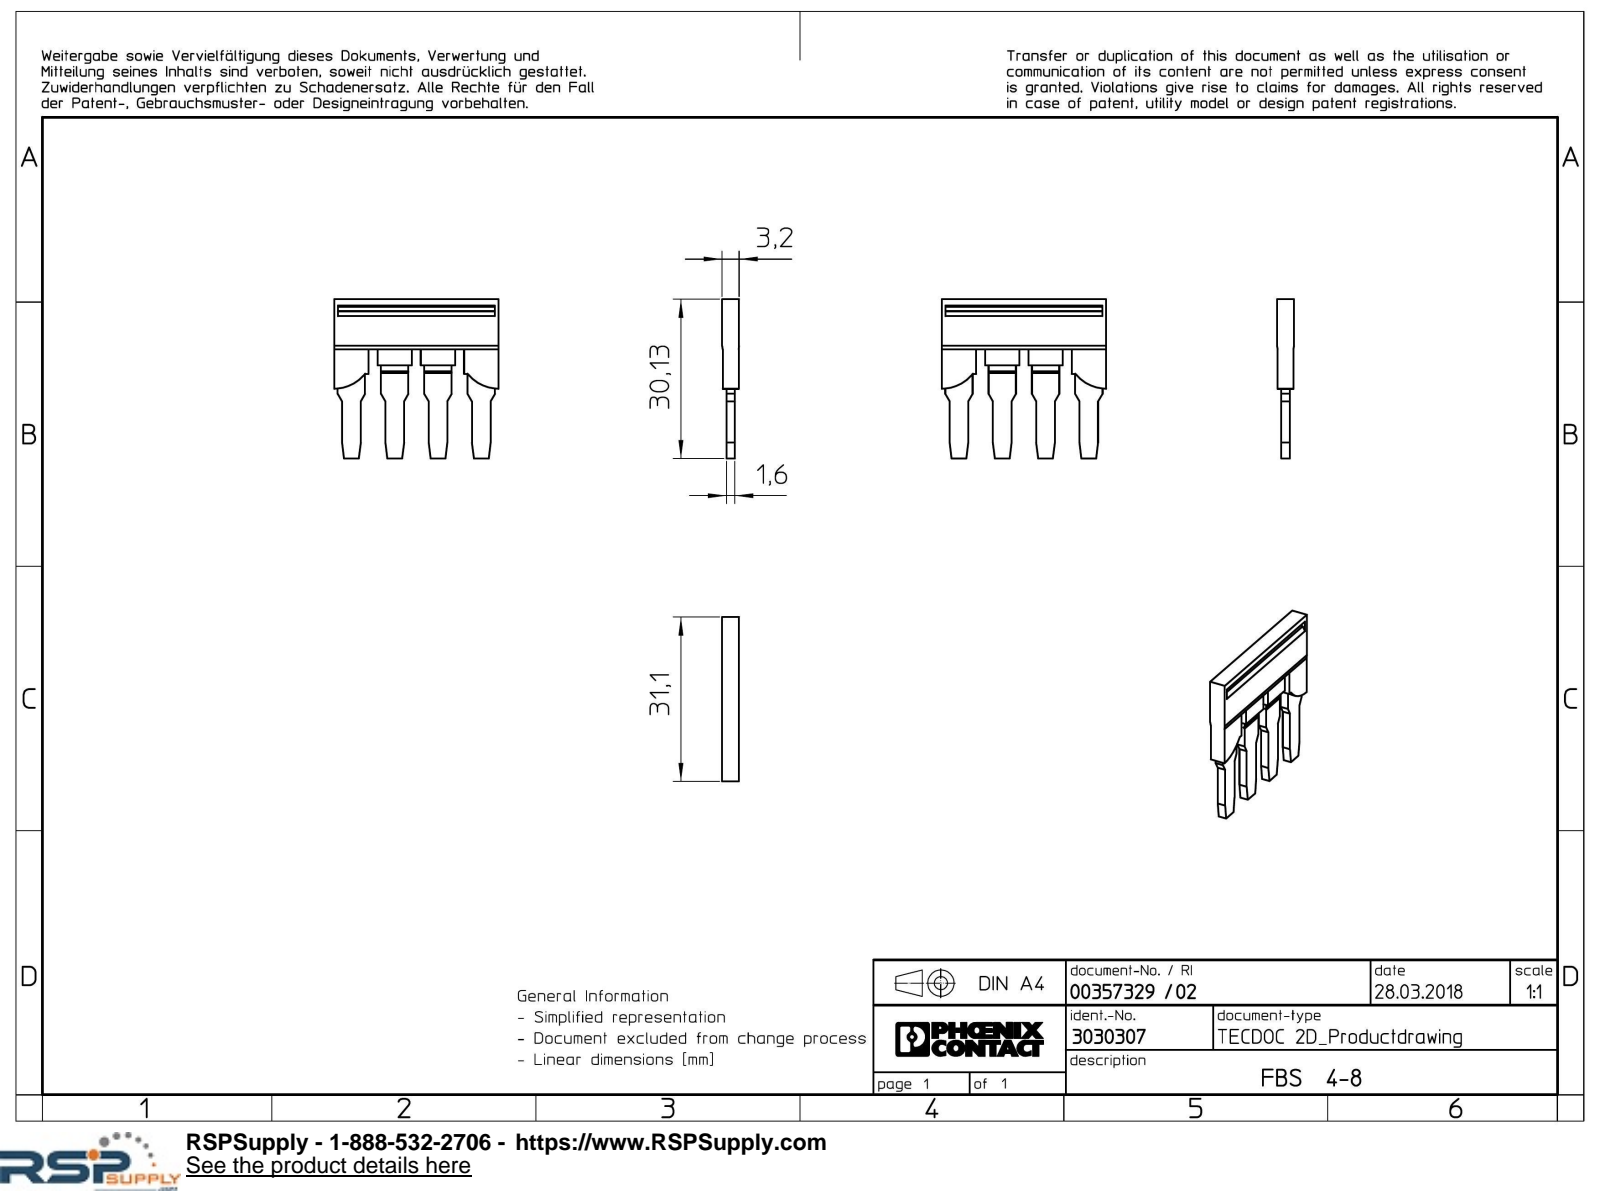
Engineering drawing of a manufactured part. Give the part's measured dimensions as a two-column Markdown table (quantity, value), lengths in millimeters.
| quantity | value |
| --- | --- |
| part name | FBS_4_8-select |
| STEP written by | Creo Elements/Direct Modeling 20.1A 29-Sep-2018 (C) Parametric Technology GmbH (AUTOMOTIVE_DESIGN) |
| units | millimeters |
| bodies | 1 solid, 98 faces (96 planar, 2 cylindrical, 0 other) |
| overall size | 31.1 × 30.12 × 3.2 |
| volume | 1 634 mm³ |
| surface area | 1 983 mm² |
| partial cylindrical surfaces (radius × count) | 7.45 × 2 |
| main face-to-face distances | 0.8, 2.4, 1.6, 3.1, 0.7, 2.3, 3.2, 3, 8.2, 16.4 |
